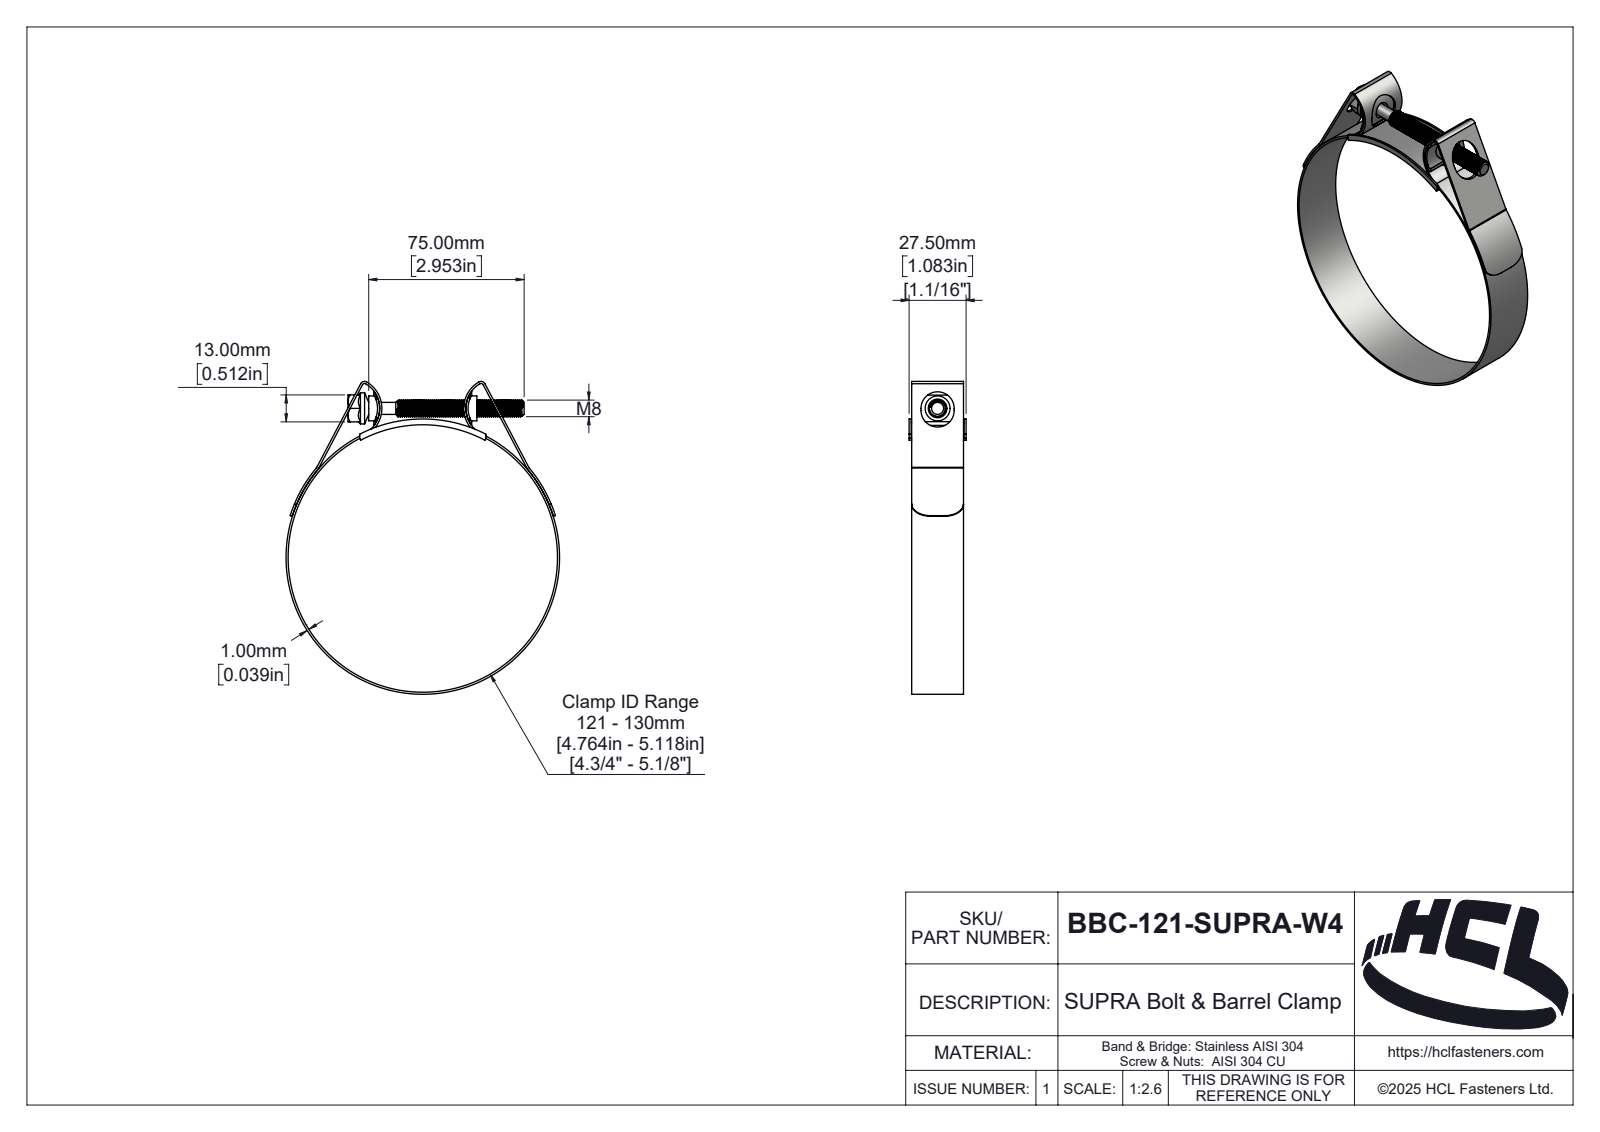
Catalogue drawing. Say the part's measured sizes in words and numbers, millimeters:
The part is named "BBC-121-SUPRA-W4". Its 3-D file was written by "SolidWorks 2025 (AUTOMOTIVE_DESIGN)". It is 5 solids with 365 faces: 46 planar, 233 cylindrical and 86 other. Overall it measures 150.92 by 132 by 27.5 millimeters. Its volume is 20 699 cubic millimeters and its surface area 37 073 square millimeters. Round holes: 1 of diameter 130. Round bosses or shafts: 1 of diameter 132, 1 of diameter 15.01, 1 of diameter 12, 1 of diameter 8, 1 of diameter 5.8. Partial cylindrical surfaces (rounded edges, fillets, slot ends): 4 of radius 1, 2 of radius 1.1, 2 of radius 2, 2 of radius 2.1, 2 of radius 3, 2 of radius 8, 2 of radius 12.65, 2 of radius 13.65. The main face-to-face distances are 1, 25, 1.25, 26.25, 26.5, 25.25, 27.5, 25.5, 13, 2.5.
